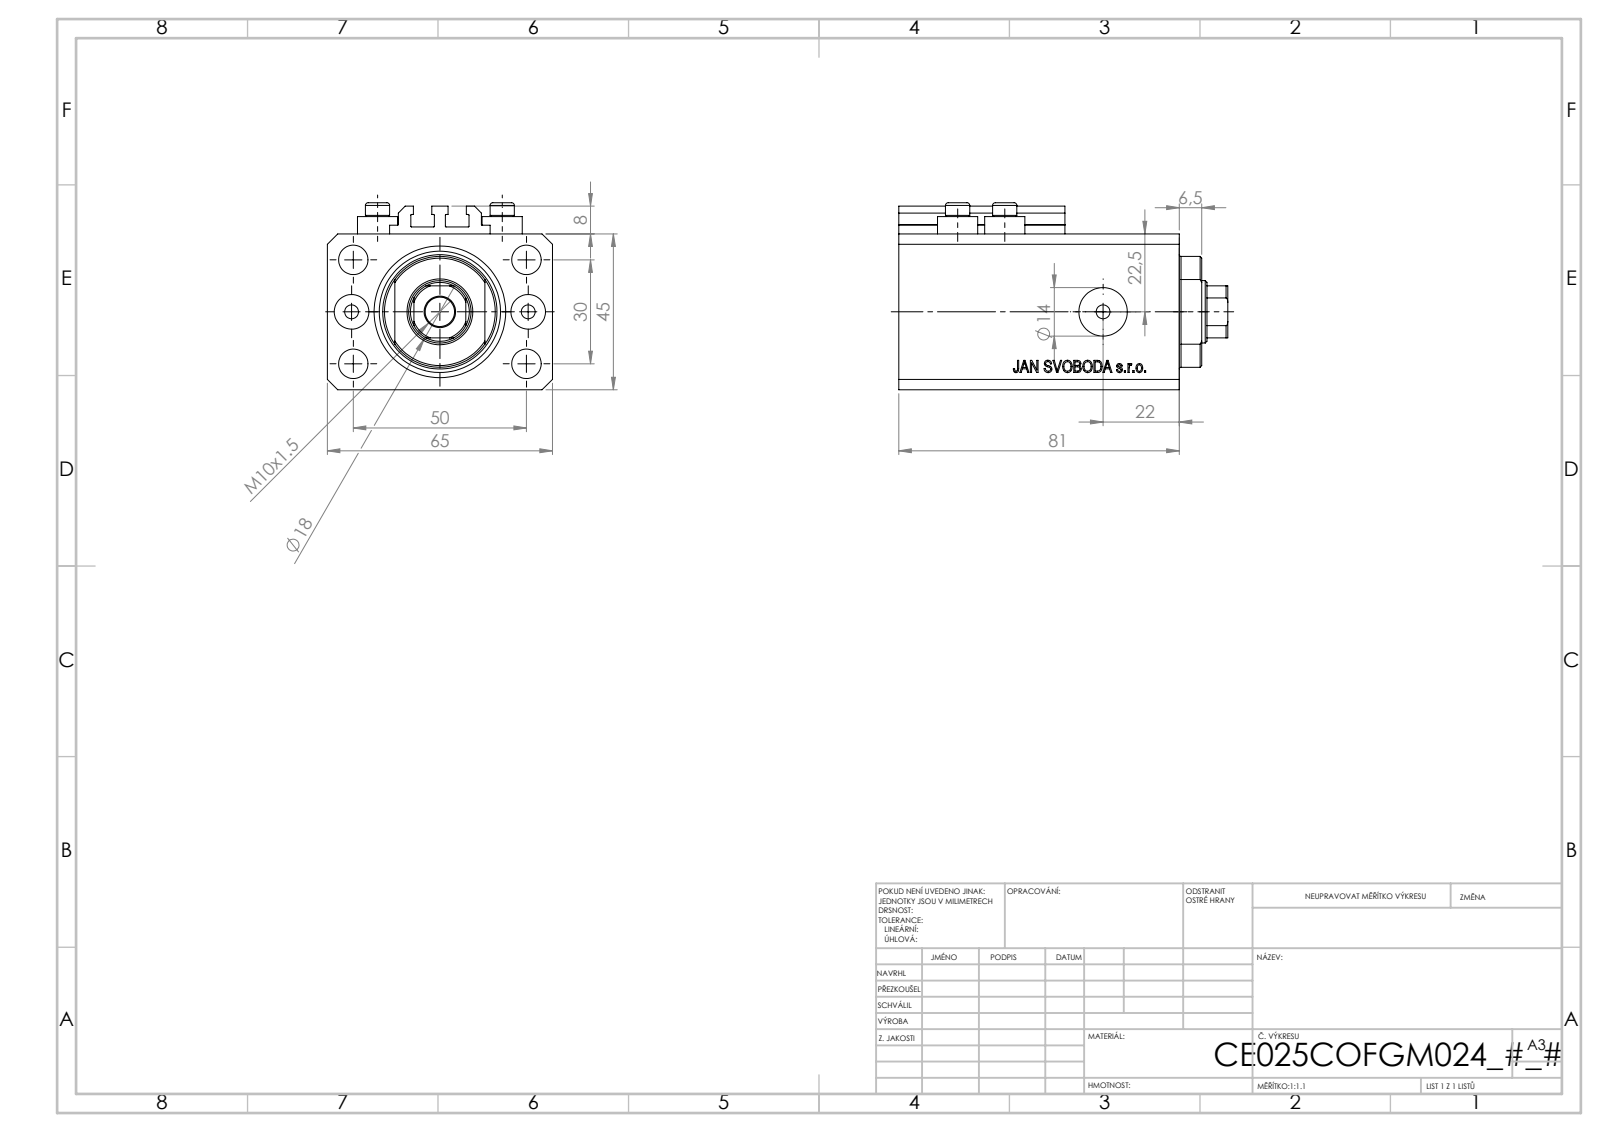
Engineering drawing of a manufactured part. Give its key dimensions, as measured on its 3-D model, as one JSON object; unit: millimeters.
{"part_name": "V250CE_C_VCP; ALLEN BOLT V250CE; V250CE_C_Body; V250CE_VC_C", "step_written_by": "SolidWorks 2019 (CONFIG_CONTROL_DESIGN)", "units": "millimeters", "bodies": {"solids": 8, "faces": 1034, "planar": 504, "cylindrical": 86, "other": 444}, "overall_size": [95, 65, 54], "volume_mm3": 222218, "surface_area_mm2": 59488, "round_holes": [[4, 8], [8.5, 5], [10, 2], [14, 2], [18, 1], [25, 1], [38, 1]], "round_bosses_or_shafts": [[11.6, 4], [7, 4]], "partial_cylinders_radius": [[0.2, 10], [8.5, 1], [16, 1]], "face_to_face_distances": [45, 65, 14, 67, 81, 6.9, 60.1, 74.1, 47, 3], "hole_center_spacings": [15.01, 29.15, 52.68, 13.6, 25.5, 30, 36, 38.48]}
